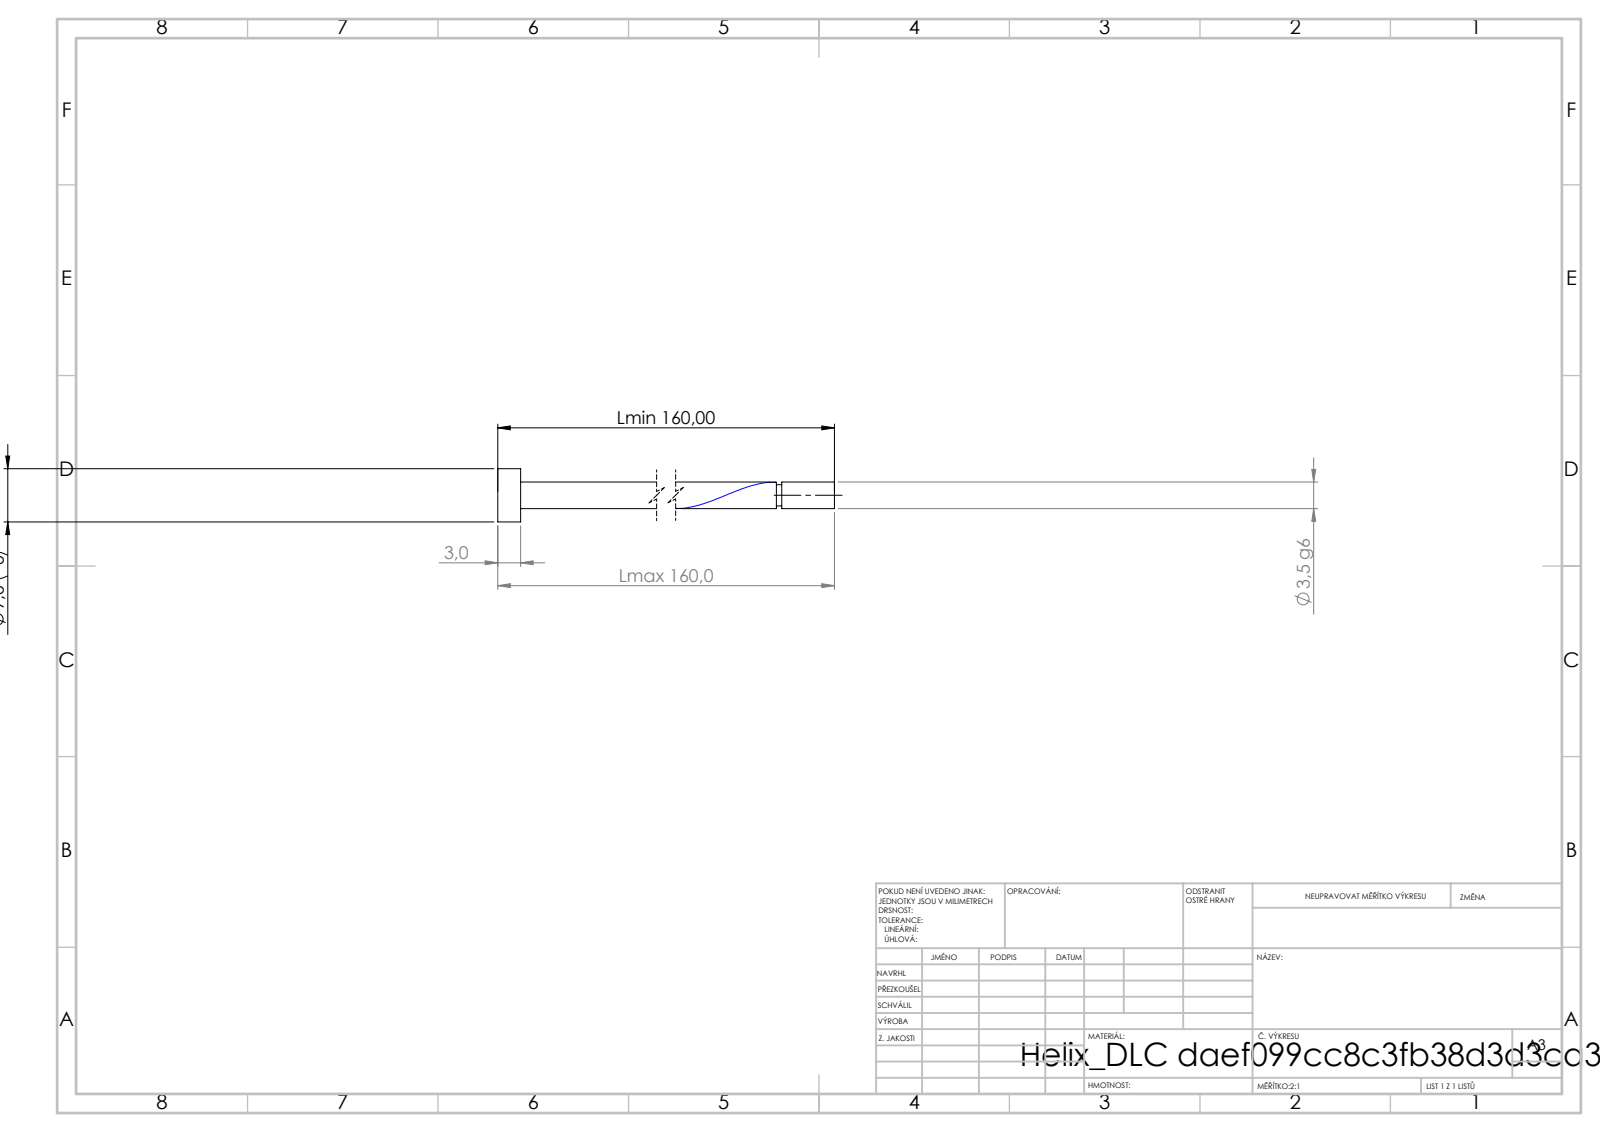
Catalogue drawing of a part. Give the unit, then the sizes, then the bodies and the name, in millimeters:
Units: millimetres
Overall size (bounding box): 160 × 7 × 7
Round bosses / shafts (diameter × count): ⌀7 ×1, ⌀3.5 ×1, ⌀2.8 ×1
Main face-to-face distances: 3, 160, 157, 153.08, 150.08, 6.92, 152.38, 149.38, 0.7, 7.62
Volume: 1 609 mm³ · Surface area: 1 904 mm²
Bodies: 1 solid, 21 faces (6 planar, 14 cylindrical, 1 other)
STEP written by: SolidWorks 2019 (CONFIG_CONTROL_DESIGN)
